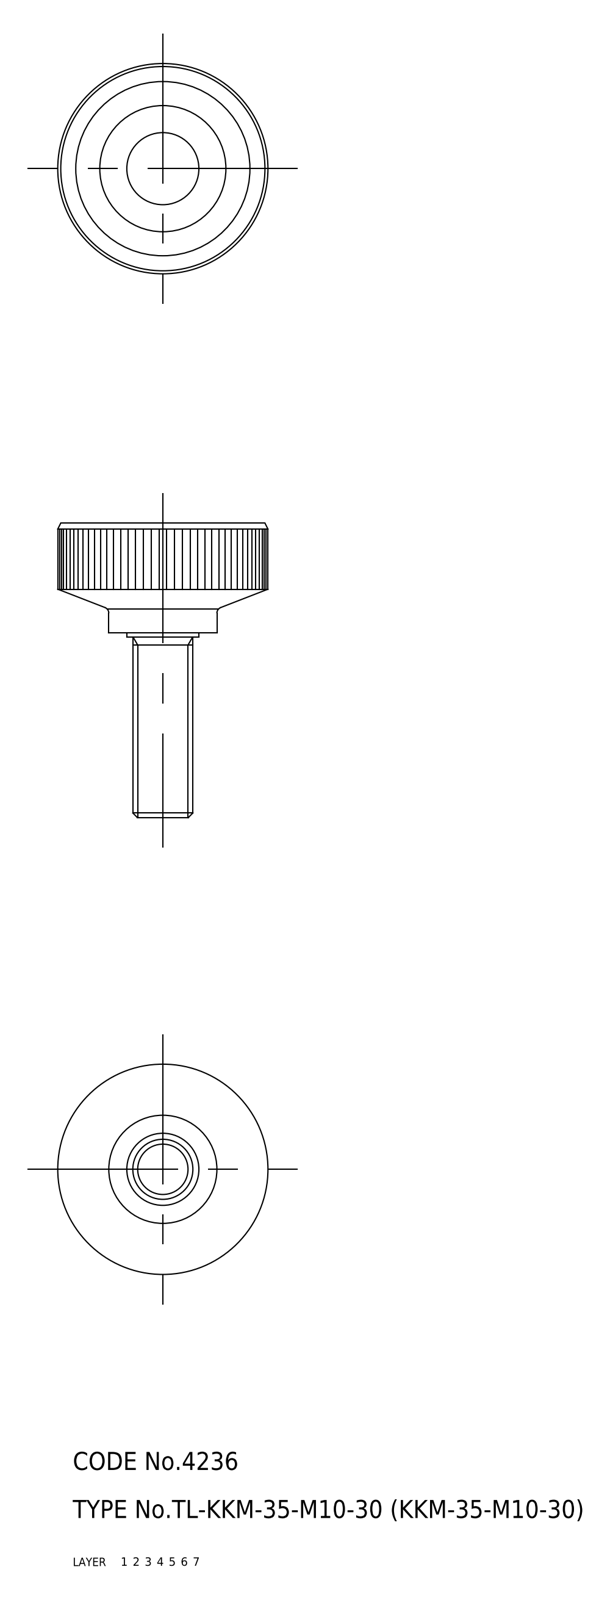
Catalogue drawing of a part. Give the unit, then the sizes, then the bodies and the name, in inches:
Units: inches
Overall size (bounding box): 1.929 × 1.378 × 1.378
Volume: 0.718 in³ · Surface area: 8.784 in²
Bodies: 2 solids, 35 faces (0 planar, 0 cylindrical, 35 other)
Part name (STEP PRODUCT): screw; knob; KKM_35_M10_30_5635_36
STEP written by: CADfix (AUTOMOTIVE_DESIGN)
